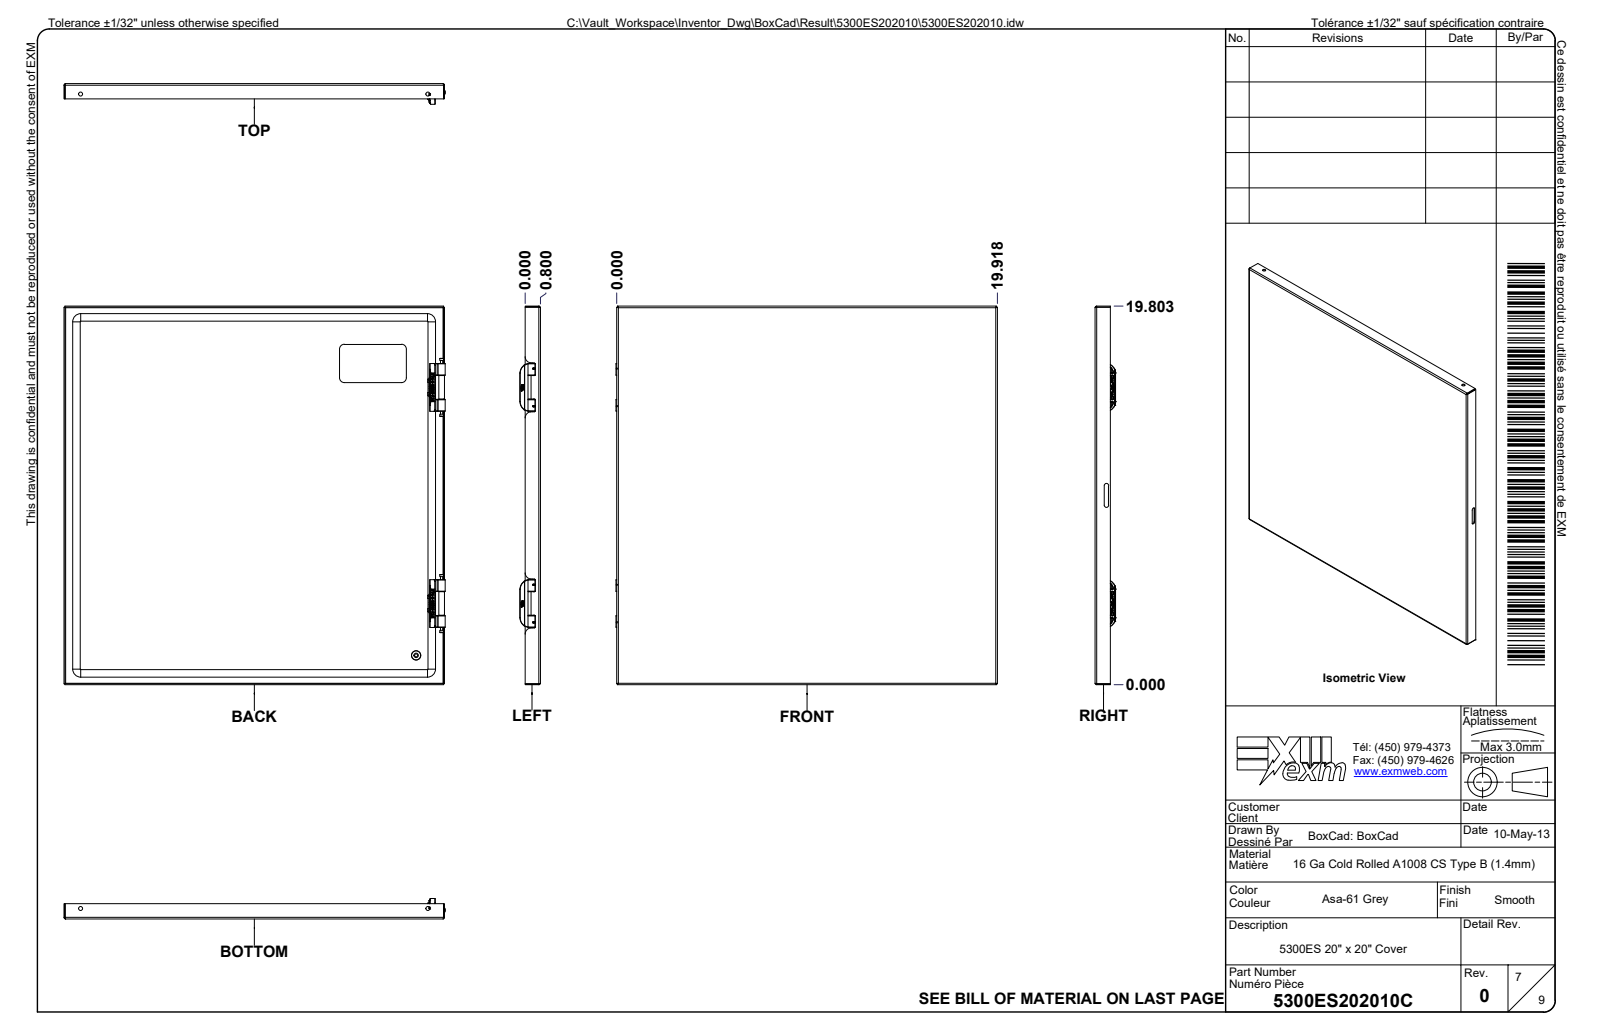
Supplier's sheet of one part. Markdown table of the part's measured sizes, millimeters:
| quantity | value |
| --- | --- |
| part name | 5300ES202010; 5300ES202010B; 5300ES202010B-P; STK-Q-16005 (+8 more) |
| STEP written by | Autodesk Inventor 2024 (AUTOMOTIVE_DESIGN) |
| units | millimeters |
| bodies | 45 solids, 5491 faces (1475 planar, 1539 cylindrical, 2477 other) |
| overall size | 531.4 × 508 × 282 |
| volume | 2 234 000 mm³ |
| surface area | 2 835 000 mm² |
| round holes (diameter × count) | 1.1 × 8, 0.8 × 6, 8 × 5, 4.5 × 4, 6.9 × 4, 7.4 × 4, 9.9 × 4, 5.1 × 3, 4.7 × 2, 5.2 × 2, 5.6 × 2, 8.4 × 2 |
| round bosses / shafts (diameter × count) | 1 × 8, 0.8 × 6, 5.9 × 5, 18.2 × 4, 7.9 × 4, 6.7 × 4, 12 × 2, 7.3 × 2 |
| partial cylindrical surfaces (radius × count) | 1 × 85, 0.5 × 79, 0.3 × 66, 0.2 × 60, 0.8 × 36, 0.4 × 30, 2.1 × 28, 0.1 × 16 |
| main face-to-face distances | 1.3, 506.7, 1.3, 279.3, 280.7, 508, 505.3, 282, 280.7, 23.5 |
| hole center spacings | 442.2, 412.8, 287.1, 412.8, 624.1, 25.4, 387.4, 413.5 |
